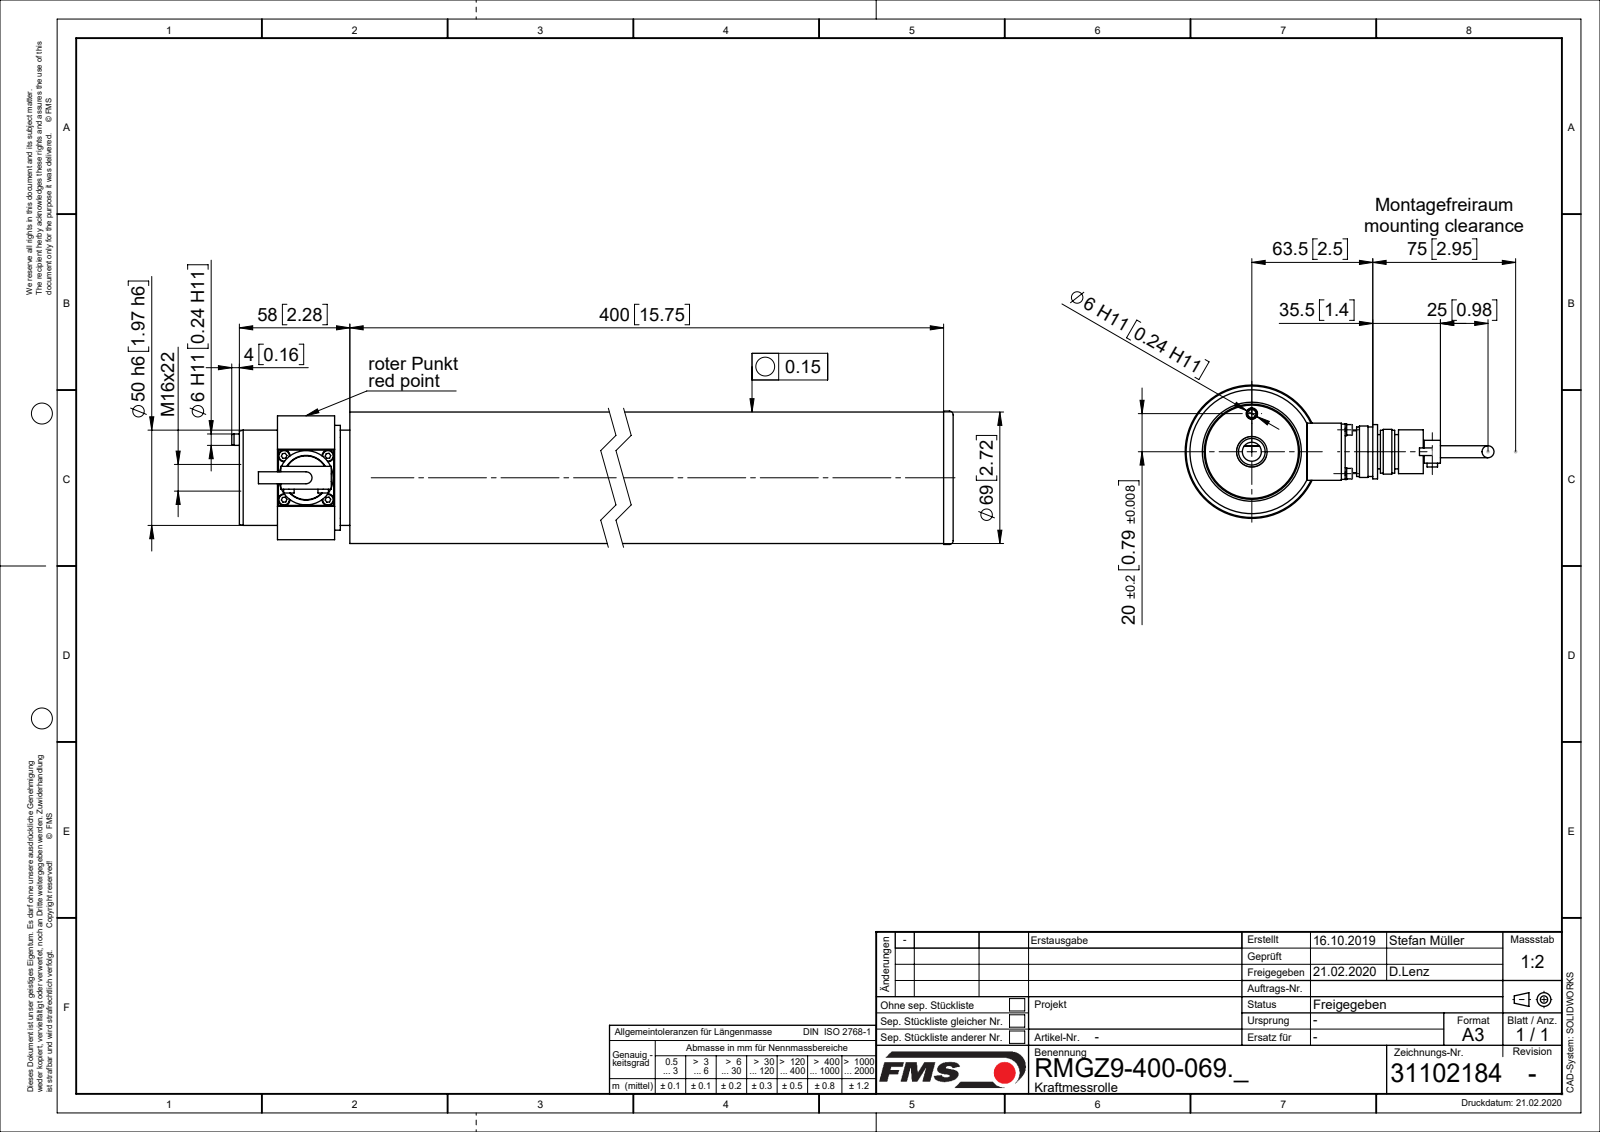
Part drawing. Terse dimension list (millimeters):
name: 47675_01; Spannstift_ISO13337_D06x12; Zyl-Schr DIN912_M3x25; Lamellenstopfen_D_070 (+8 more)
written by: SolidWorks 2018 (CONFIG_CONTROL_DESIGN)
unit: mm
bodies: 31 solids, 597 faces (172 planar, 259 cylindrical, 166 other)
size: 467 × 162.15 × 70
volume: 853 834 mm³; area: 305 921 mm²
holes: 6× ⌀2.5, 4× ⌀3.1, 4× ⌀3.4, 1× ⌀3.3, 1× ⌀5, 1× ⌀6, 1× ⌀10, 1× ⌀12, 1× ⌀14, 1× ⌀17, 1× ⌀22, 1× ⌀23
bosses: 6× ⌀5.5, 4× ⌀6.2, 4× ⌀3, 4× ⌀2.5, 1× ⌀70, 1× ⌀69, 1× ⌀65, 1× ⌀58
rounds: 4× R0.1, 4× R11, 2× R4.19, 2× R4.25, 1× R17.5, 1× R22.2, 1× R25.37
face distances: 50, 2, 3, 5, 35, 133, 408, 20, 275, 142
hole spacings: 16.26, 23, 24.85, 32.53, 18.14, 20, 25.59, 37.16
